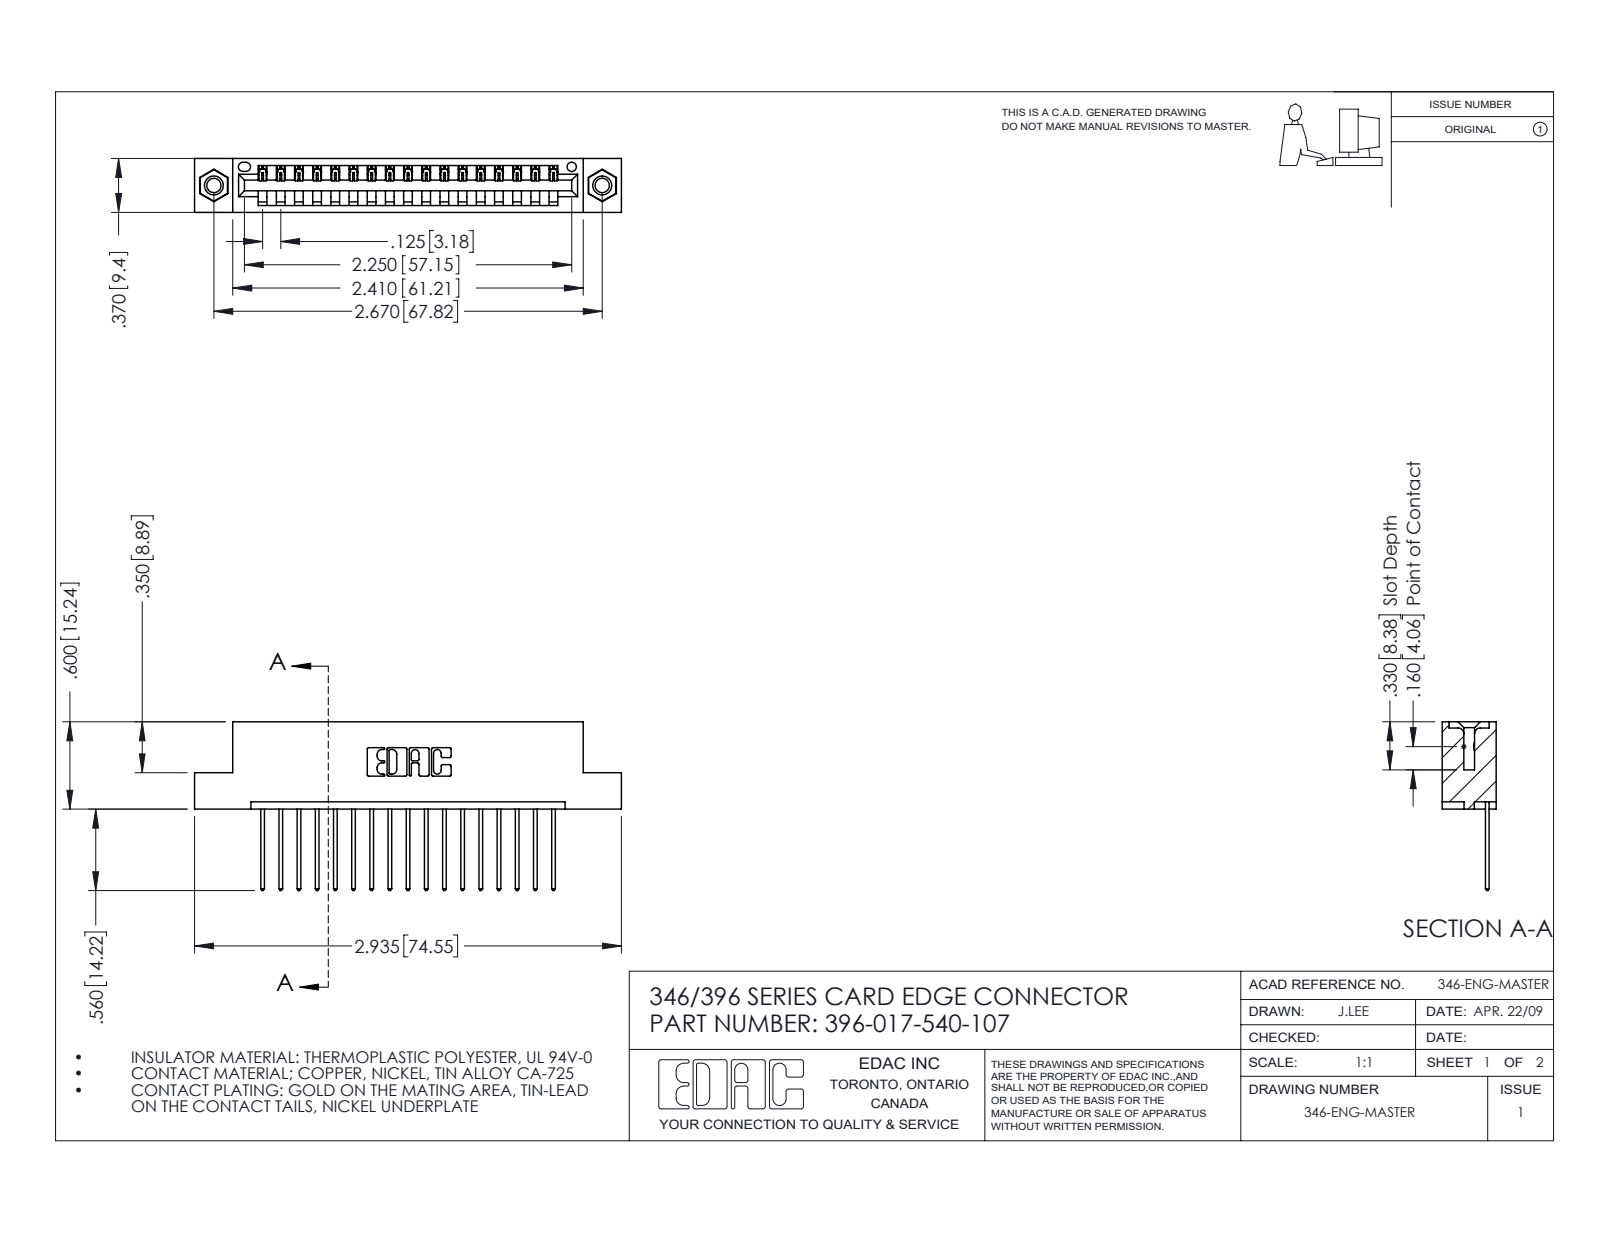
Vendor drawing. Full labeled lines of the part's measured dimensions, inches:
Part name (STEP PRODUCT): 346 Part_Flush Mounting Lugs - 0.156 Dia-TI; 345-250-001_345-250-005-103; 345-292-001_345-293-140; 396-017-540-107
STEP written by: SolidWorks 2016 (CONFIG_CONTROL_DESIGN)
Units: inches
Bodies: 20 solids, 1168 faces (788 planar, 364 cylindrical, 16 other)
Overall size (bounding box): 2.935 × 1.16 × 0.37
Volume: 0.426 in³ · Surface area: 13.41 in²
Round holes (diameter × count): ⌀0.098 ×2, ⌀0.125 ×2, ⌀0.156 ×2, ⌀0.064 ×1
Round bosses / shafts (diameter × count): ⌀0.155 ×2
Partial cylindrical surfaces — rounded edges, fillets, slot ends (radius × count): R0.006 ×34, R0.01 ×34, R0.01 ×22, R0.007 ×6, R0.031 ×6, R0.026 ×3, R0.031 ×2, R0.04 ×2
Main face-to-face distances: 0.048, 0.322, 0.25, 0.37, 0.072, 0.298, 0.025, 0.148, 0.222, 0.1
Hole centre spacings: 0.246, 2.463, 2.67
